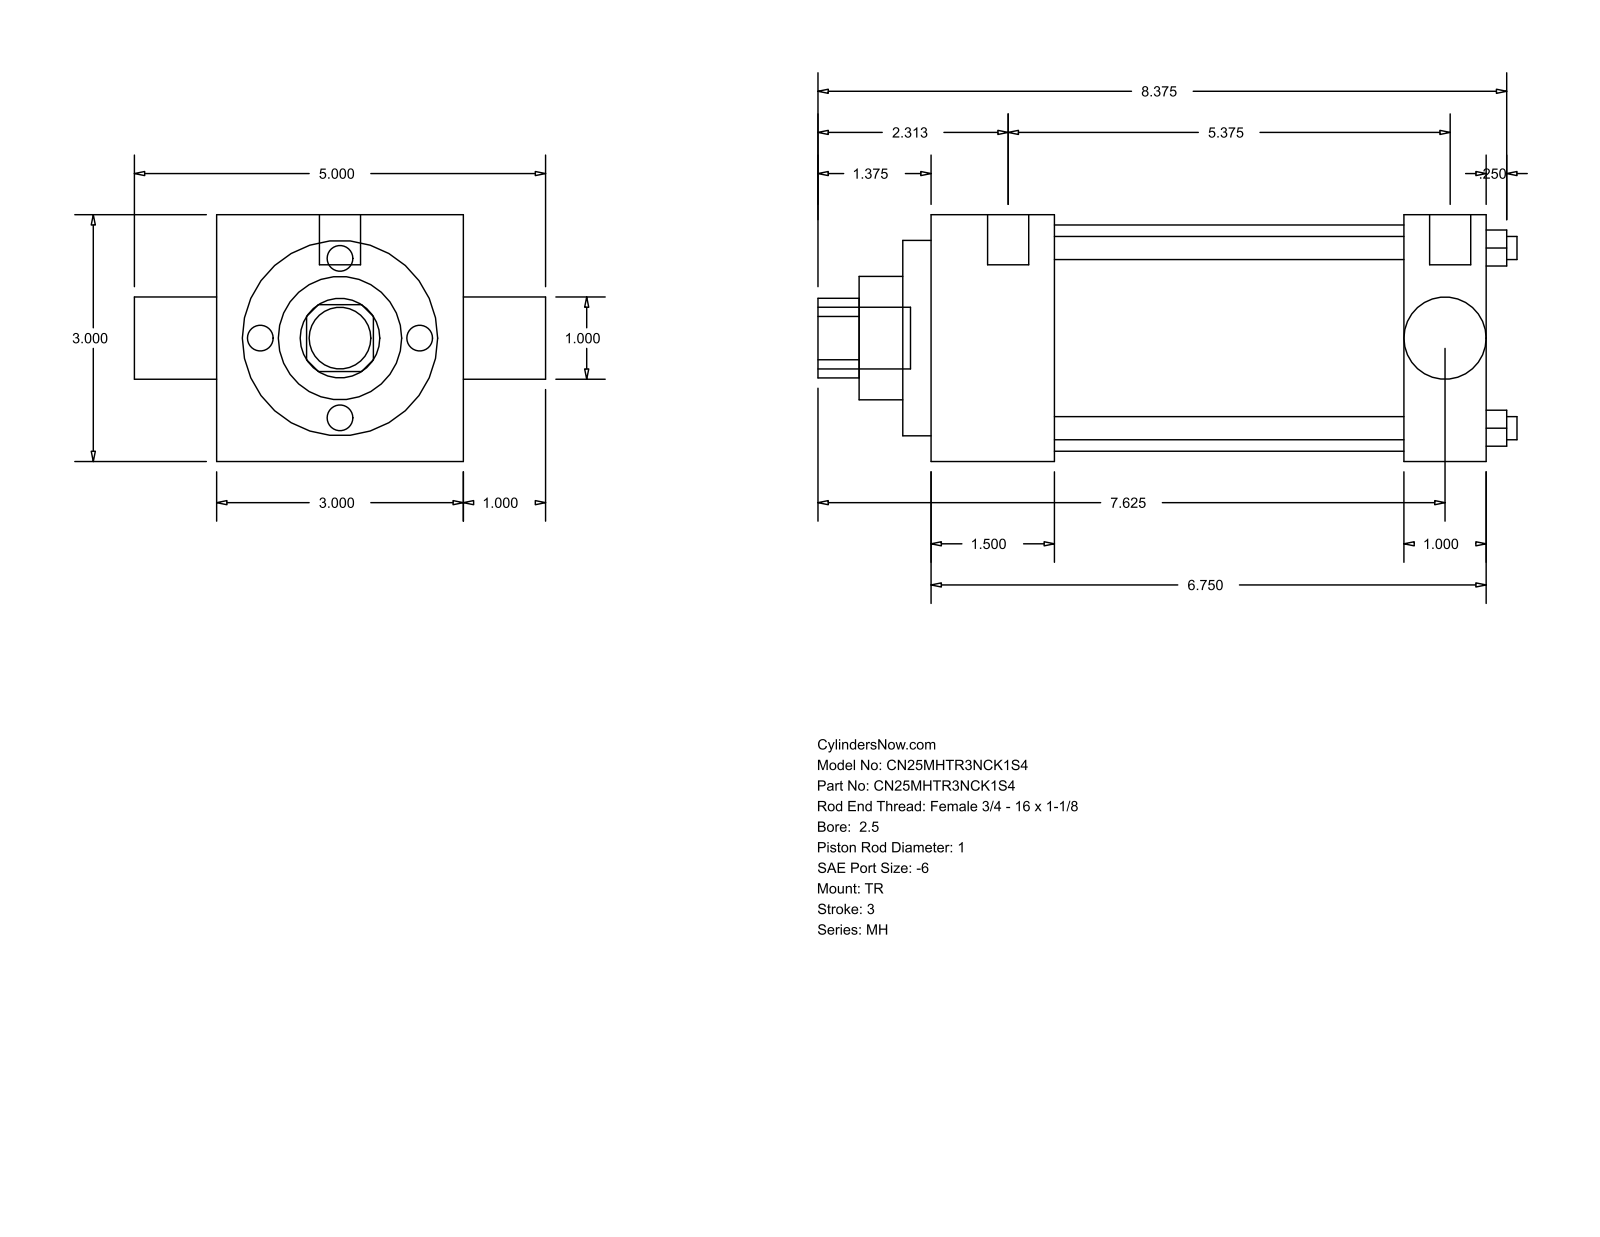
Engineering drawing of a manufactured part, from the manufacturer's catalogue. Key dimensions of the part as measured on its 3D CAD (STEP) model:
Part name (STEP PRODUCT): MH_TR__0250_1
STEP written by: GSSL Pune (CONFIG_CONTROL_DESIGN)
Units: millimetres
Bodies: 0 solids, 86 faces (61 planar, 25 cylindrical, 0 other)
Overall size (bounding box): 215.9 × 127 × 76.2
Round holes (diameter × count): ⌀7.14 ×4, ⌀25.35 ×1, ⌀25.4 ×1, ⌀38.1 ×1, ⌀60.33 ×1, ⌀69.85 ×1
Round bosses / shafts (diameter × count): ⌀5.56 ×3, ⌀12.7 ×2, ⌀19.05 ×1
Partial cylindrical surfaces — rounded edges, fillets, slot ends (radius × count): R12.29 ×1
Main face-to-face distances: 76.2, 171.46, 38.11, 133.35, 146.05, 107.94, 25.41, 8.73, 46.84, 154.78
Hole centre spacings: 39.33, 55.62, 78.66
